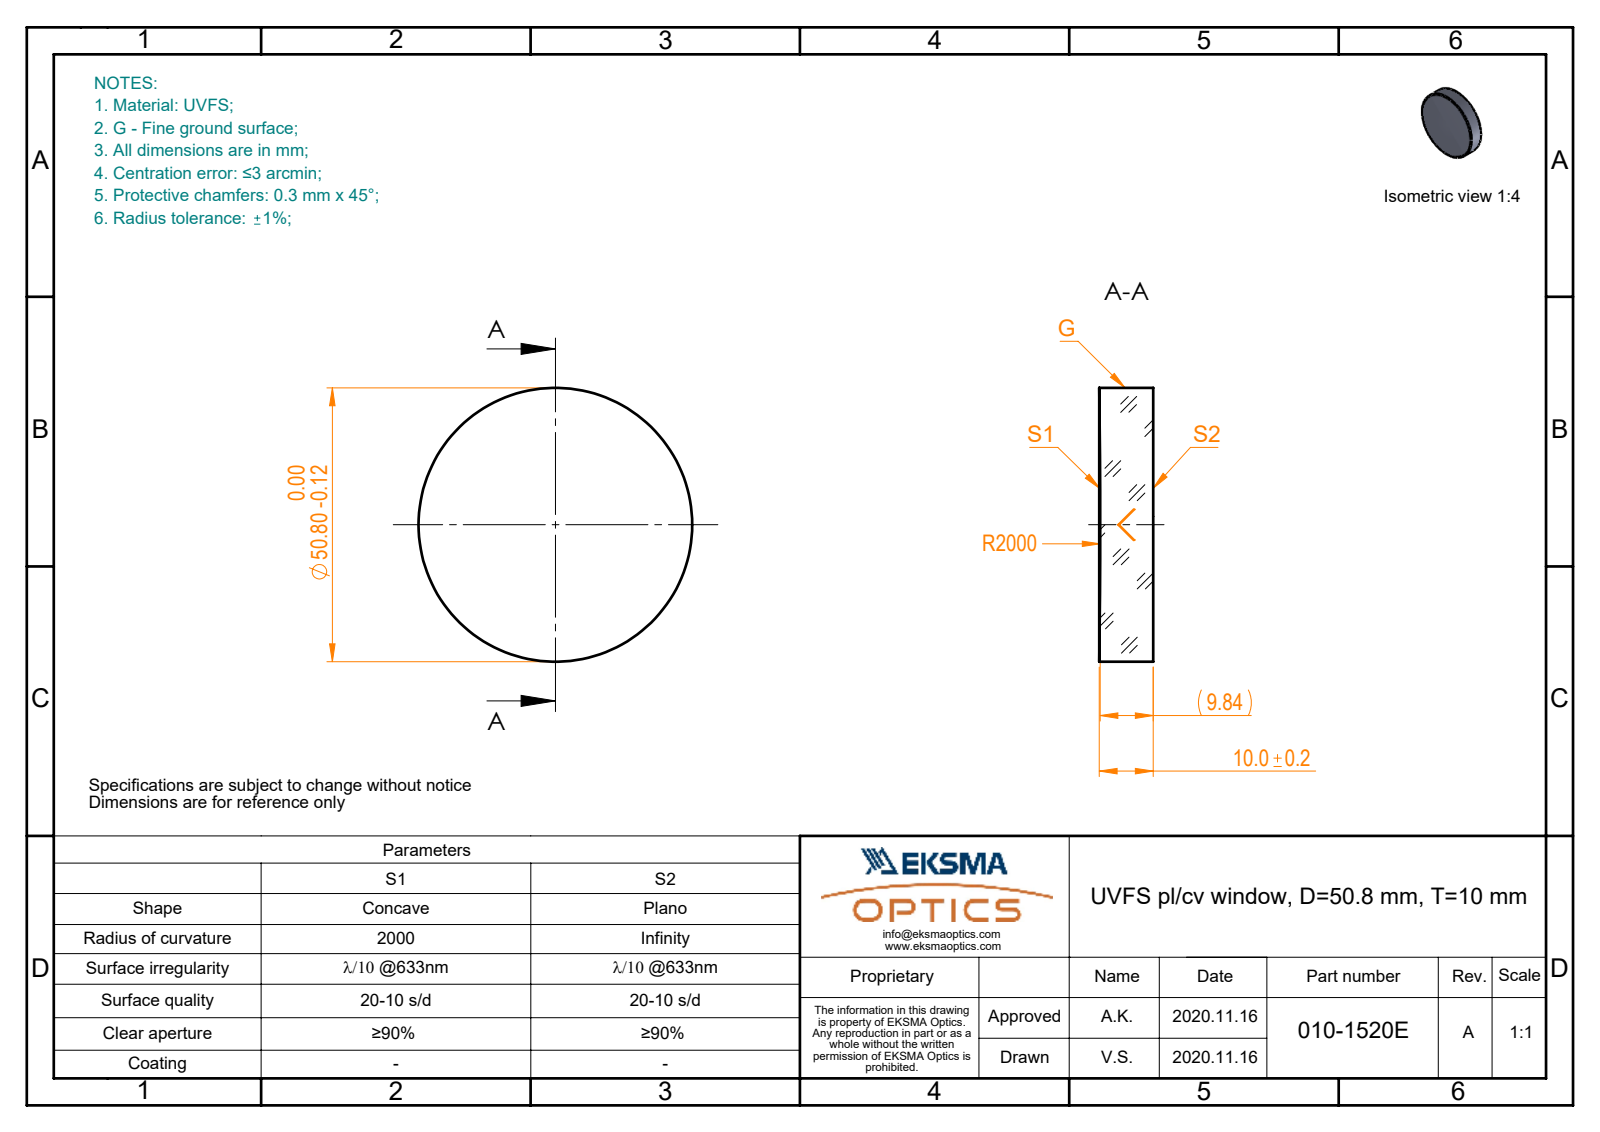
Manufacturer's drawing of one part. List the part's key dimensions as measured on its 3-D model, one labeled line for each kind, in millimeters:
Part name (STEP PRODUCT): 010-1520E_UVFS_PCV_window
STEP written by: SolidWorks 2019 (CONFIG_CONTROL_DESIGN)
Units: millimetres
Bodies: 1 solid, 5 faces (1 planar, 2 cylindrical, 2 other)
Overall size (bounding box): 50.8 × 50.8 × 10
Volume: 20 105 mm³ · Surface area: 5 650 mm²
Round bosses / shafts (diameter × count): ⌀50.8 ×1
